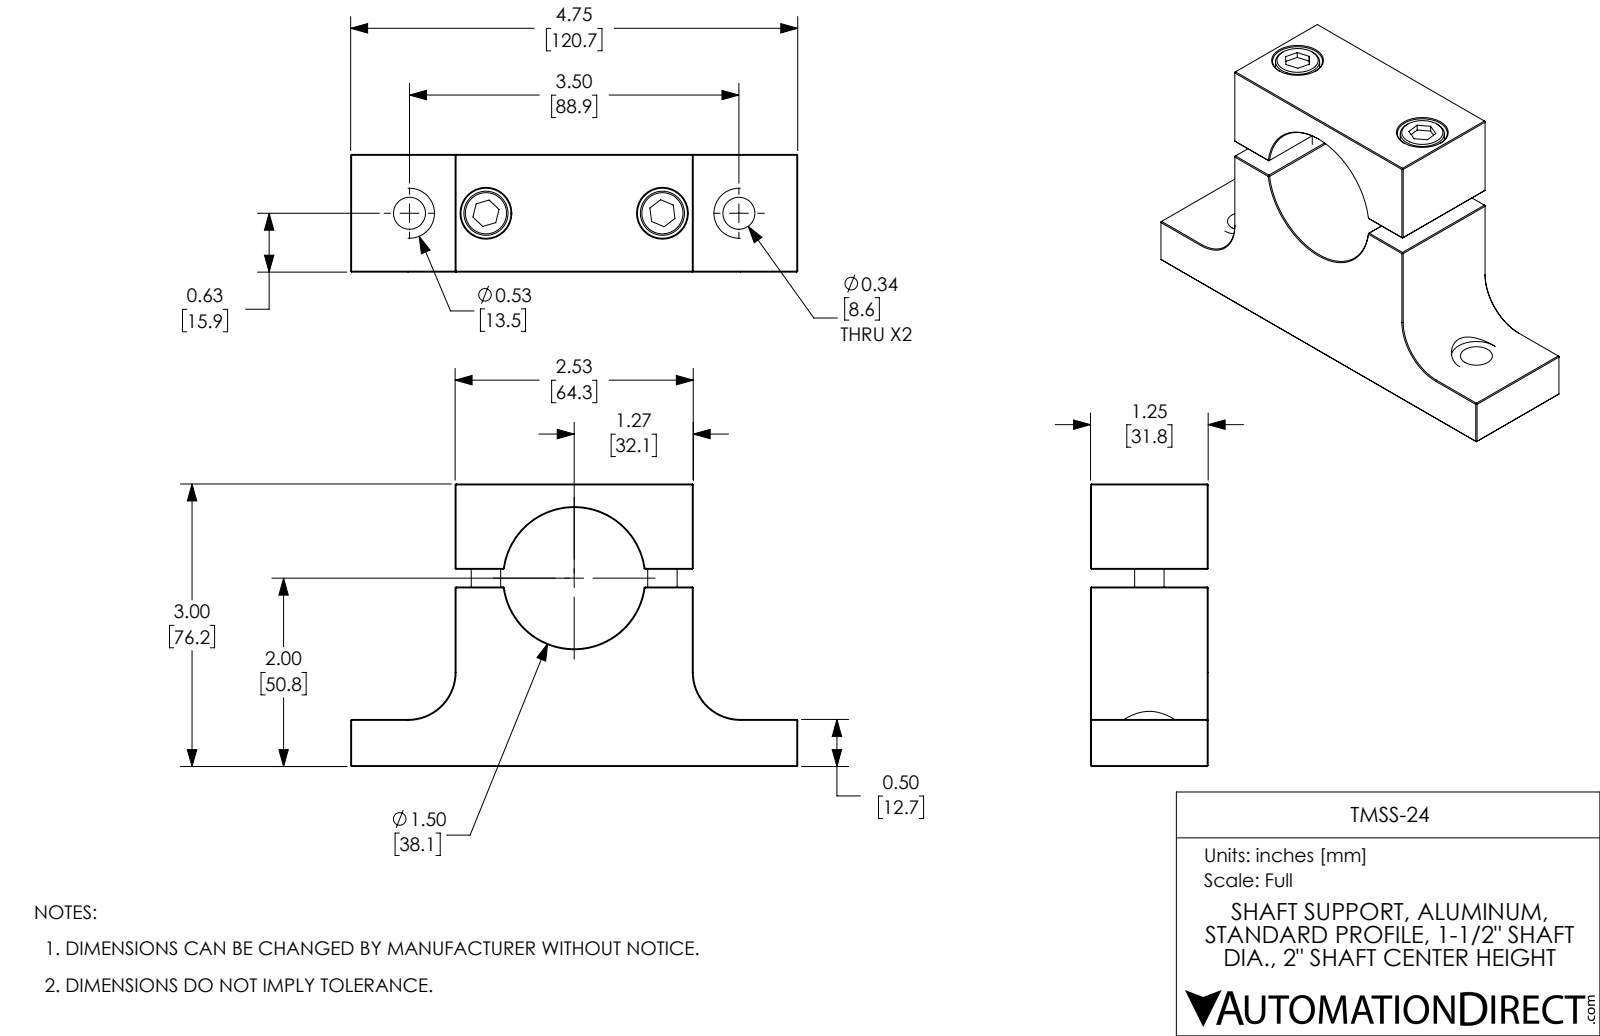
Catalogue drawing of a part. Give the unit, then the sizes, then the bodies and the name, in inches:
Units: inches
Overall size (bounding box): 4.75 × 3 × 1.25
Round holes (diameter × count): ⌀0.252 ×2, ⌀0.332 ×2, ⌀0.34 ×2, ⌀0.531 ×2, ⌀1.5 ×1
Round bosses / shafts (diameter × count): ⌀0.469 ×2, ⌀0.313 ×2
Partial cylindrical surfaces — rounded edges, fillets, slot ends (radius × count): R0.266 ×2, R0.5 ×2
Main face-to-face distances: 1.25, 3, 2.53, 0.5, 2.5, 1.11, 3.64, 1.906, 1.406, 1.094
Hole centre spacings: 0.813, 2.687, 1.875, 3.5
Volume: 8.32 in³ · Surface area: 49.34 in²
Bodies: 4 solids, 168 faces (110 planar, 34 cylindrical, 24 other)
Part name (STEP PRODUCT): TMSS-24
STEP written by: SolidWorks 2017 (AUTOMOTIVE_DESIGN)
